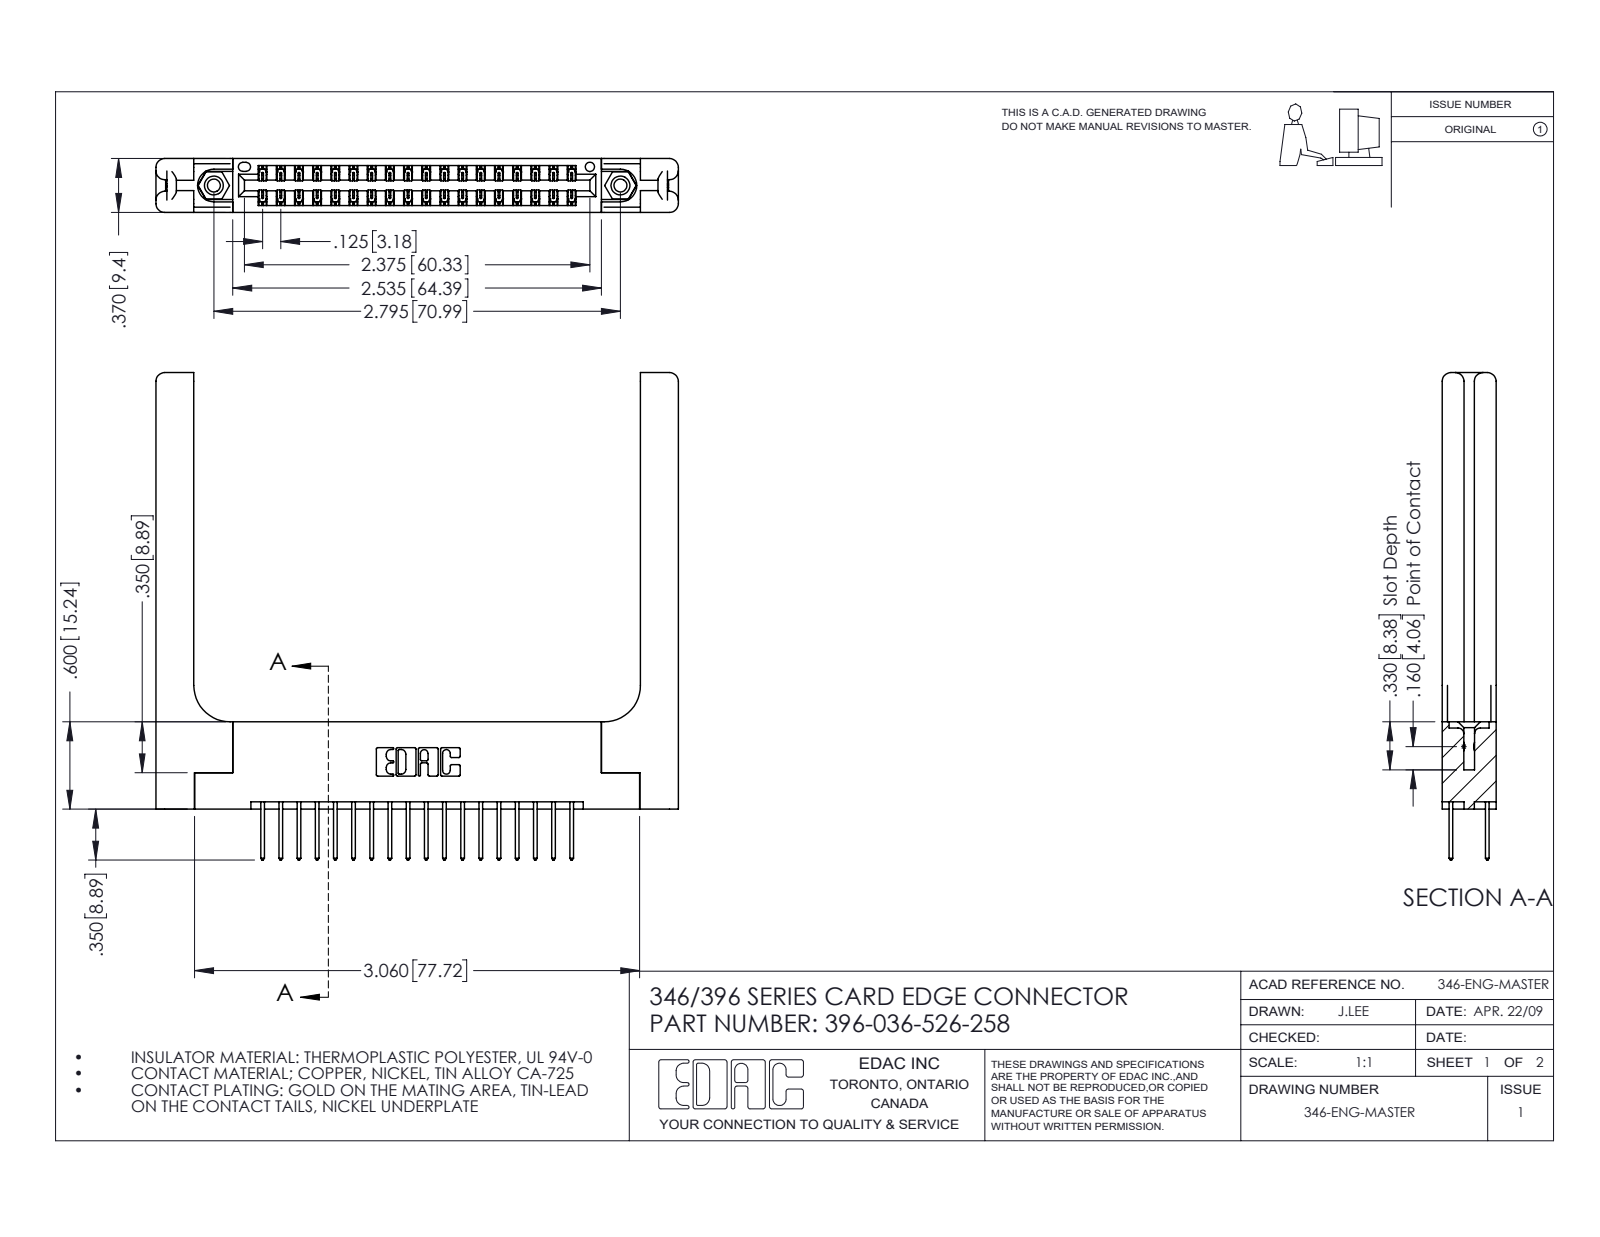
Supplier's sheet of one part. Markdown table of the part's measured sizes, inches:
| quantity | value |
| --- | --- |
| part name | 345-292-001_345-293-126; 346-220-058_345-220-058; 345-250-001_345-250-001-102; 396-036-526-258 (+1 more) |
| STEP written by | SolidWorks 2016 (CONFIG_CONTROL_DESIGN) |
| units | inches |
| bodies | 41 solids, 2250 faces (1484 planar, 706 cylindrical, 60 other) |
| overall size | 3.591 × 3.35 × 0.37 |
| volume | 0.992 in³ |
| surface area | 26.21 in² |
| round holes (diameter × count) | 0.089 × 2, 0.125 × 2, 0.156 × 2, 0.064 × 1 |
| round bosses / shafts (diameter × count) | 0.155 × 2 |
| partial cylindrical surfaces (radius × count) | 0.006 × 54, 0.01 × 36, 0.01 × 22, 0.06 × 16, 0.007 × 6, 0.031 × 6, 0.026 × 3, 0.014 × 2 |
| main face-to-face distances | 0.37, 0.072, 0.048, 0.322, 0.148, 0.15, 0.25, 0.025, 0.298, 0.077 |
| hole center spacings | 0.246, 2.588, 2.795 |
